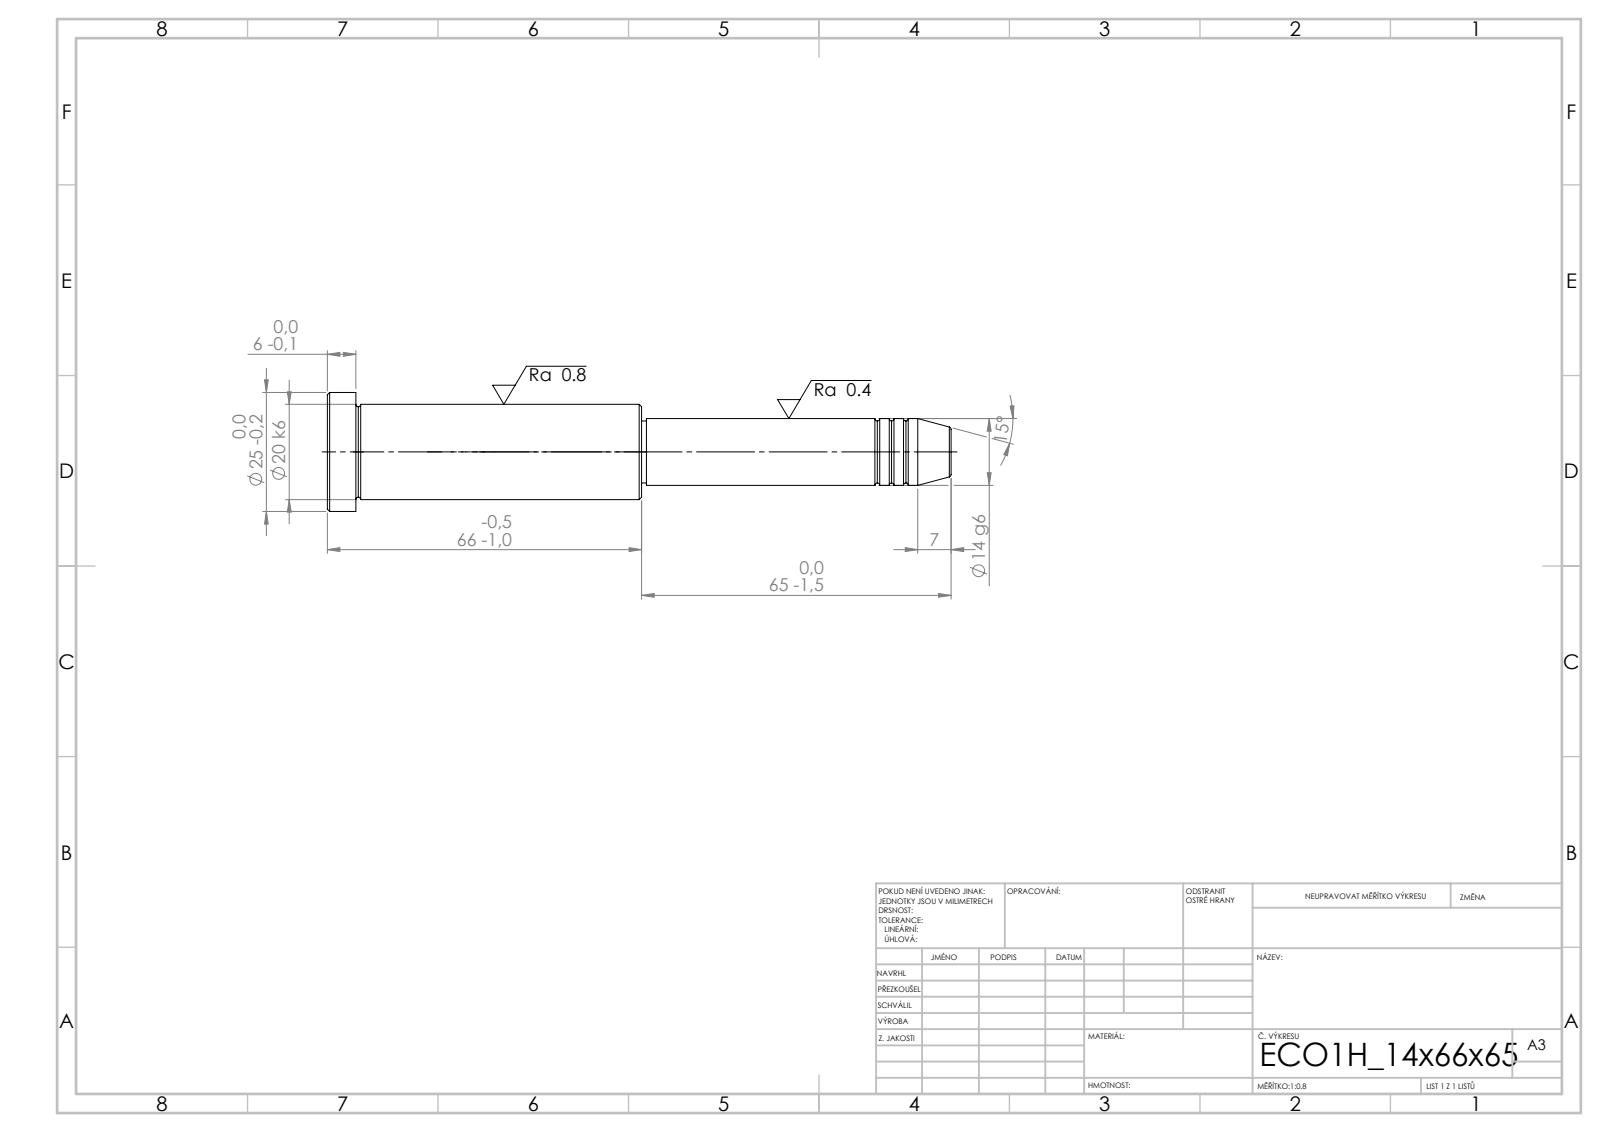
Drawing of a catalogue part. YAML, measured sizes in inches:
step_written_by: "SolidWorks 2019 (CONFIG_CONTROL_DESIGN)"
units: inches
bodies: {solids: 1, faces: 43, planar: 5, cylindrical: 14, other: 24}
overall_size: [5.157, 0.984, 0.984]
volume: 1.918
surface_area: 12.51
round_bosses_or_shafts:
  - {diameter: 0.984, count: 1}
  - {diameter: 0.787, count: 1}
  - {diameter: 0.551, count: 1}
  - {diameter: 0.512, count: 1}
face_to_face_distances: [0.236, 2.362, 2.598, 2.559, 4.921, 5.157, 2.52, 0.039, 2.402, 2.638]
